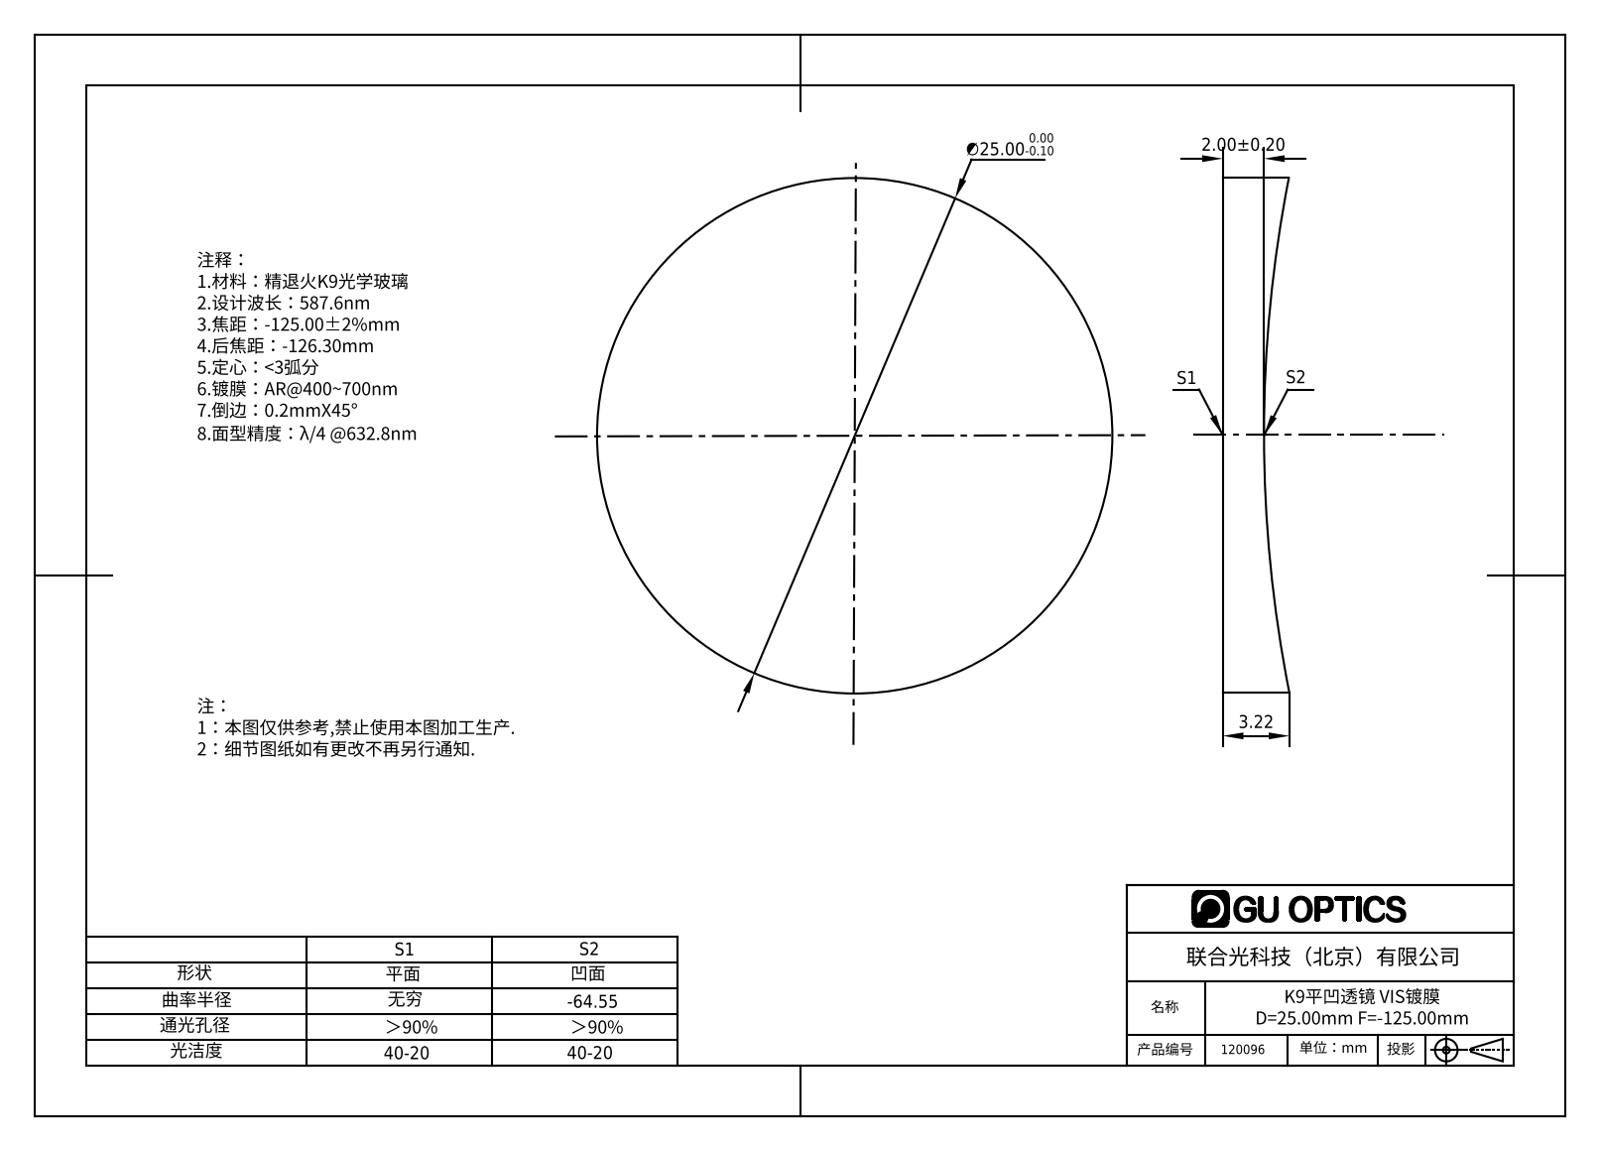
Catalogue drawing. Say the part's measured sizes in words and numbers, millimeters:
The part is named "120036". Its 3-D file was written by "SolidWorks 2016 (AUTOMOTIVE_DESIGN)". It is 1 solid with 5 faces: 1 planar, 2 cylindrical and 2 other. Overall it measures 25 by 25 by 3.21 millimeters. Its volume is 1 278 cubic millimeters and its surface area 1 239 square millimeters. Round bosses or shafts: 1 of diameter 25.
